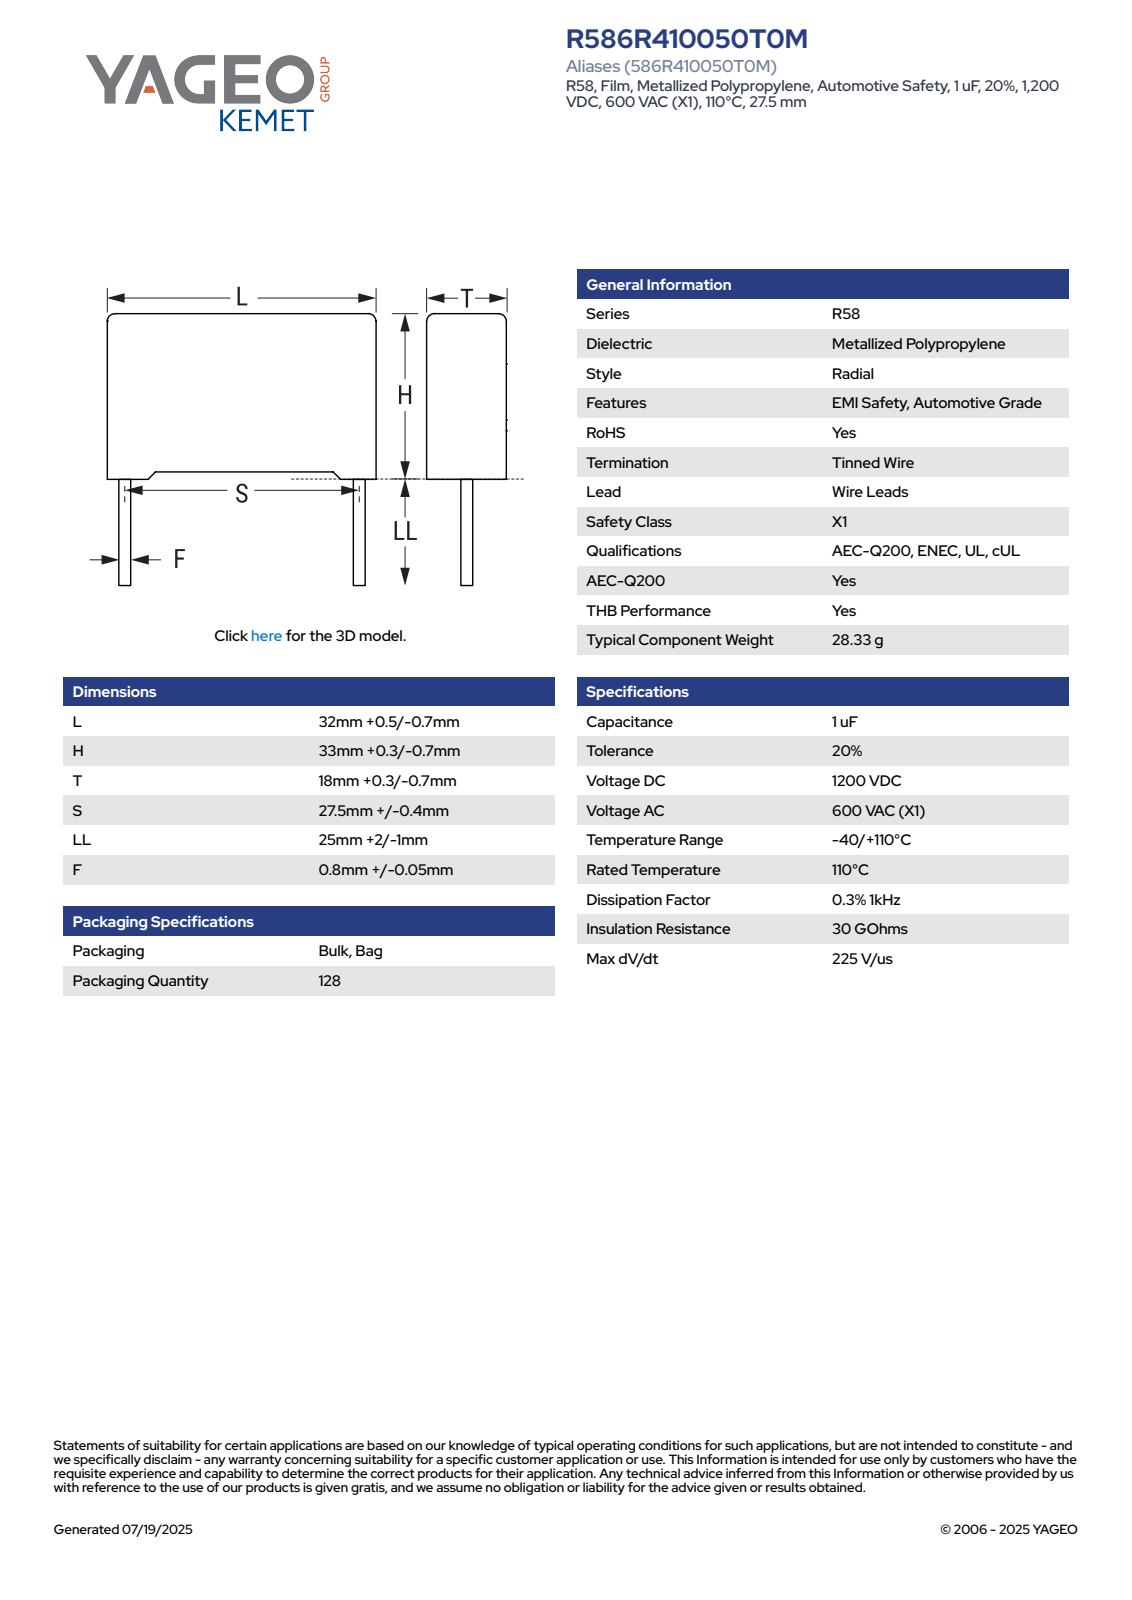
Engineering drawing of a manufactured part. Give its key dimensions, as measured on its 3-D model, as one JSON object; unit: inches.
{"part_name": "CFR_RB2_32X33X18_L32.5H33.3T18.3S27.5LL27F0.85", "step_written_by": "SolidWorks 2021 (AUTOMOTIVE_DESIGN)", "units": "inches", "bodies": {"solids": 4, "faces": 85, "planar": 77, "cylindrical": 8, "other": 0}, "overall_size": [2.374, 1.28, 0.72], "volume_in3": 1.175, "surface_area_in2": 7.387, "round_bosses_or_shafts": [[0.033, 2]], "partial_cylinders_radius": [[0.02, 4]], "face_to_face_distances": [0.72, 1.28, 1.266, 0.016, 1.281, 0.03, 0.045, 1.311, 0.043, 1.237]}
